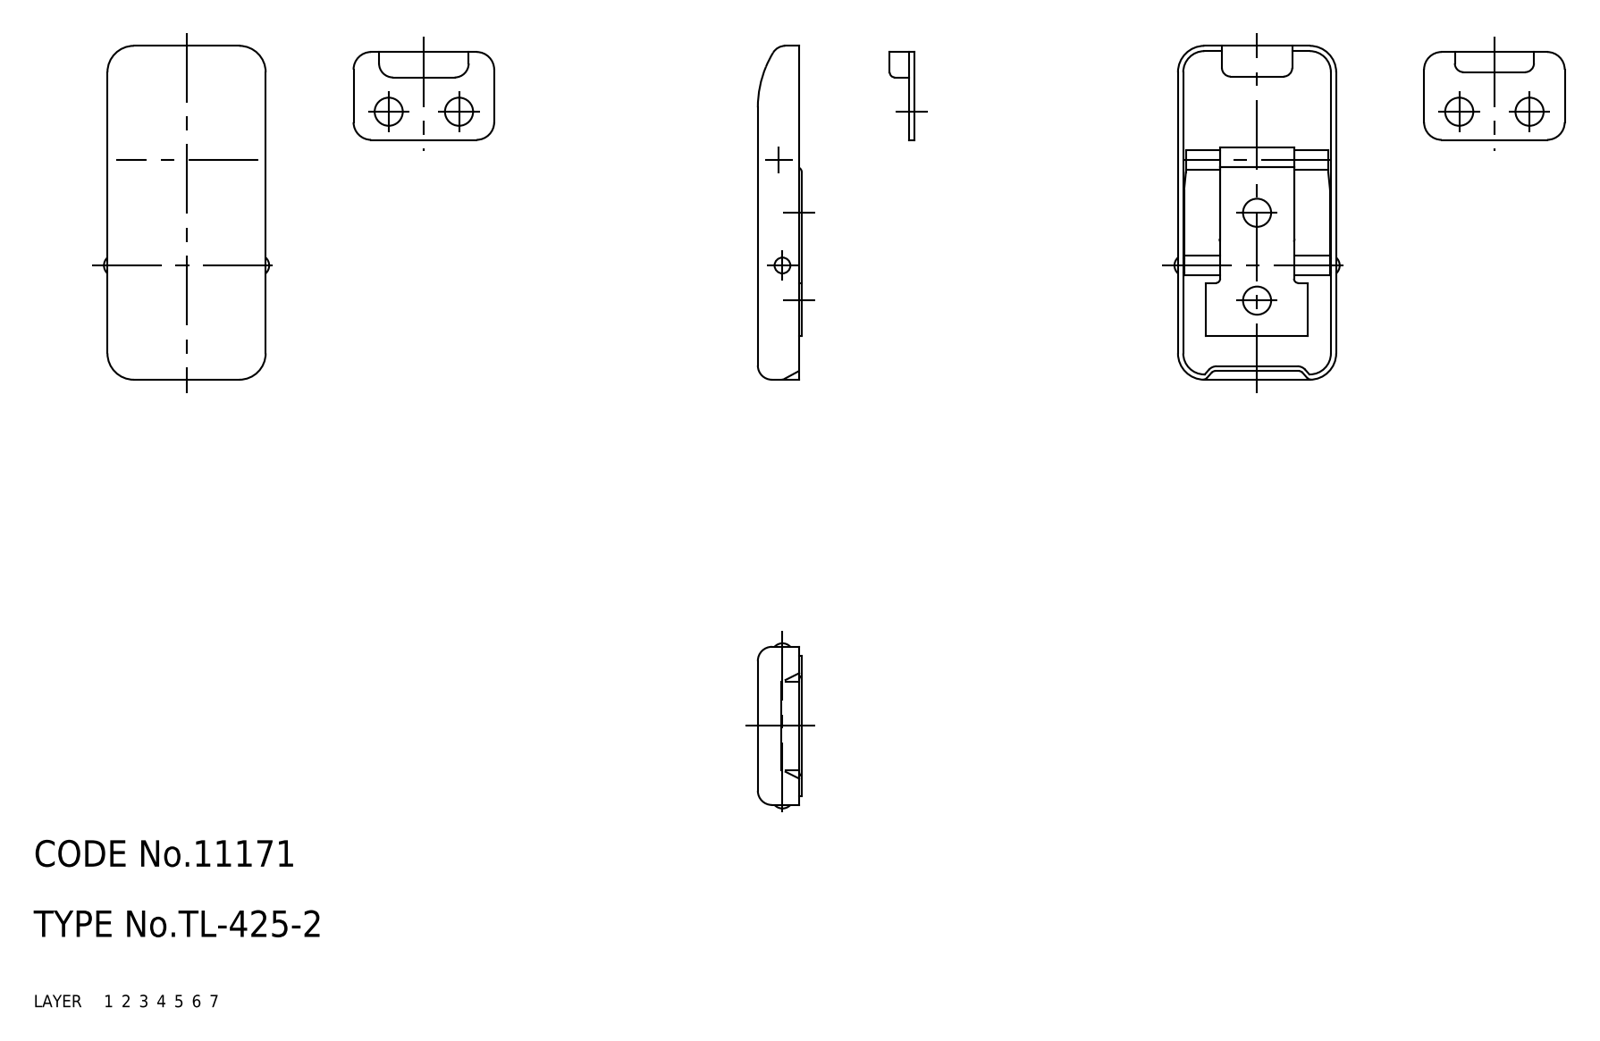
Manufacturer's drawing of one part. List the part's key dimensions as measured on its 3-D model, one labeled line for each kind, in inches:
Part name (STEP PRODUCT): a; TL_425_2
STEP written by: SolidWorks 2015 (AUTOMOTIVE_DESIGN)
Units: inches
Bodies: 1 solid, 194 faces (86 planar, 86 cylindrical, 22 other)
Overall size (bounding box): 1.496 × 0.791 × 0.197
Volume: 0.064 in³ · Surface area: 5.379 in²
Round holes (diameter × count): ⌀0.126 ×4
Round bosses / shafts (diameter × count): ⌀0.091 ×2, ⌀0.063 ×2, ⌀0.11 ×1
Partial cylindrical surfaces — rounded edges, fillets, slot ends (radius × count): R0.024 ×15, R0.039 ×12, R0.063 ×6, R0.079 ×4, R0.094 ×4, R0.118 ×4, R0.02 ×2, R0.047 ×2
Main face-to-face distances: 0.024, 0.173, 0.15, 0.197, 0.685, 0.161, 0.709, 0.661, 0.126, 0.559
Hole centre spacings: 0.48, 0.861, 0.315, 0.394
